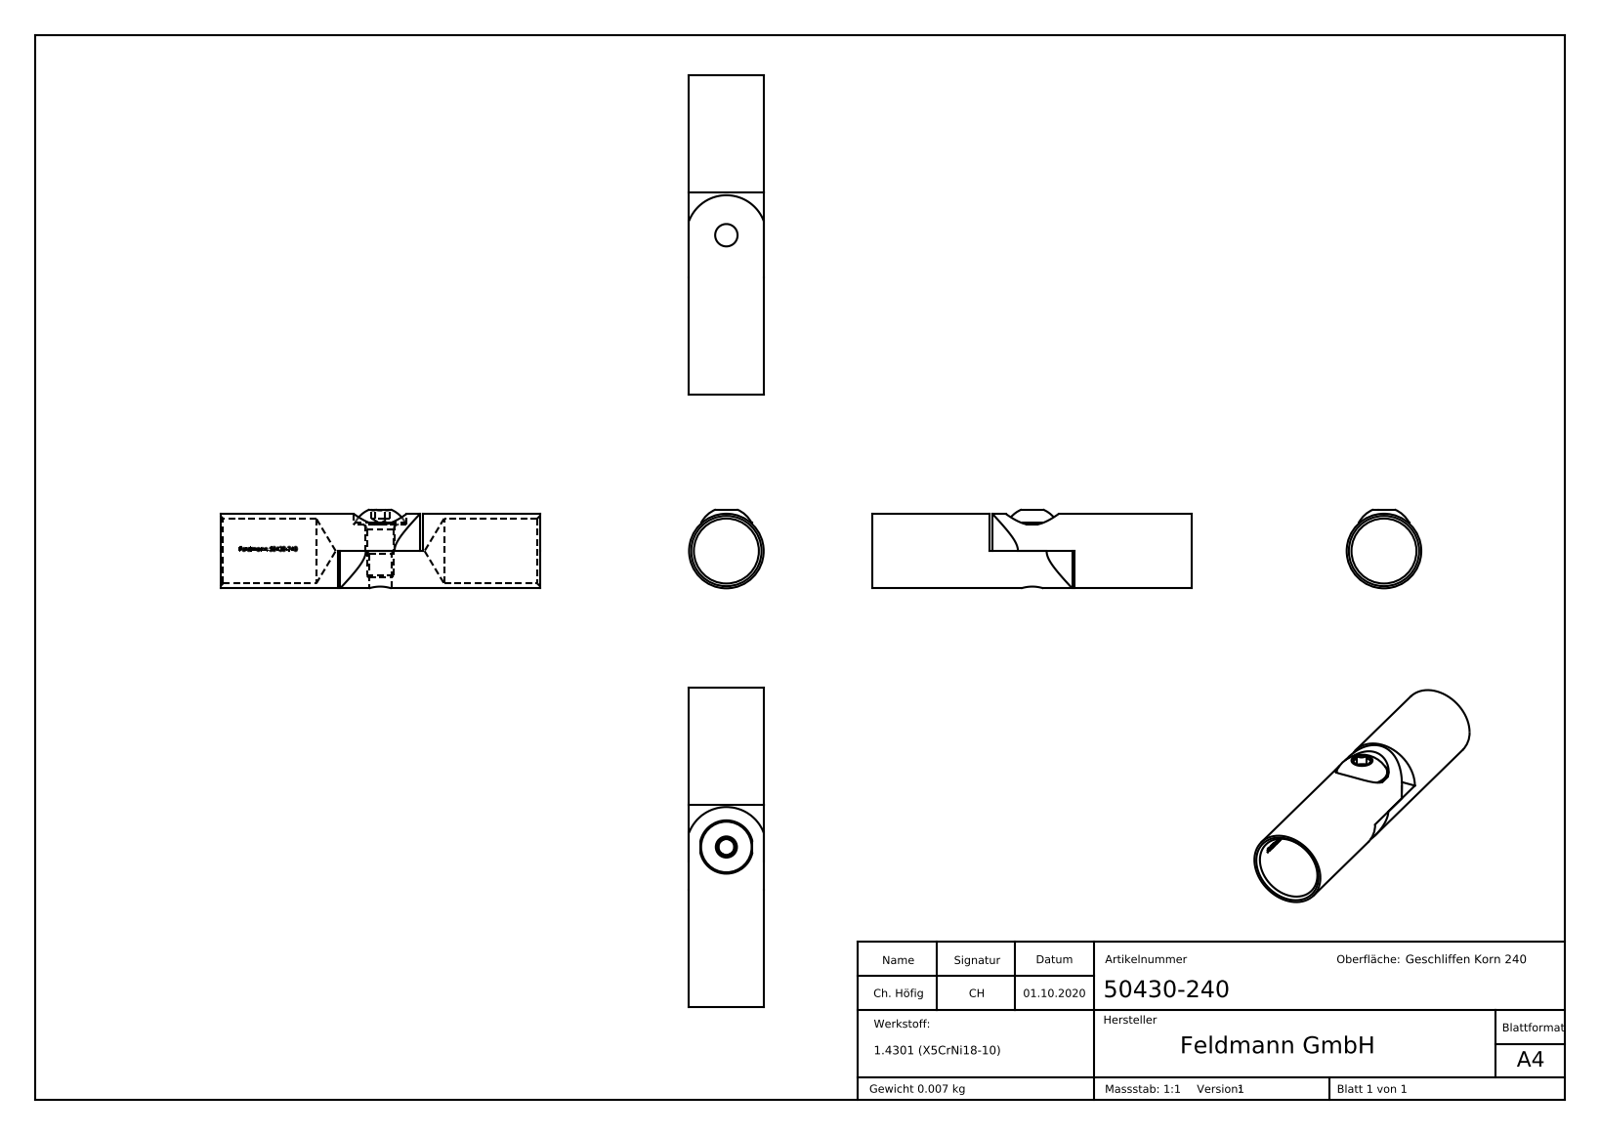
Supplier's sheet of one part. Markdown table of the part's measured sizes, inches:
| quantity | value |
| --- | --- |
| part name | 50430-240; DIN 7380; 504XX-240 Teil1; DIN 7380_DIN 7380 M5x10 (+3 more) |
| STEP written by | SolidWorks 2018 (CONFIG_CONTROL_DESIGN) |
| units | inches |
| bodies | 3 solids, 292 faces (116 planar, 48 cylindrical, 128 other) |
| overall size | 2.362 × 0.583 × 0.551 |
| volume | 0.274 in³ |
| surface area | 8.42 in² |
| round holes (diameter × count) | 0.165 × 1, 0.217 × 1, 0.394 × 1, 0.48 × 1 |
| round bosses / shafts (diameter × count) | 0.551 × 1, 0.374 × 1, 0.197 × 1 |
| partial cylindrical surfaces (radius × count) | 0.244 × 1, 0.295 × 1 |
| main face-to-face distances | 0.197, 0.63, 0.866, 1.496, 2.362, 0.394, 0.118, 0.504, 0.307, 0.11 |
